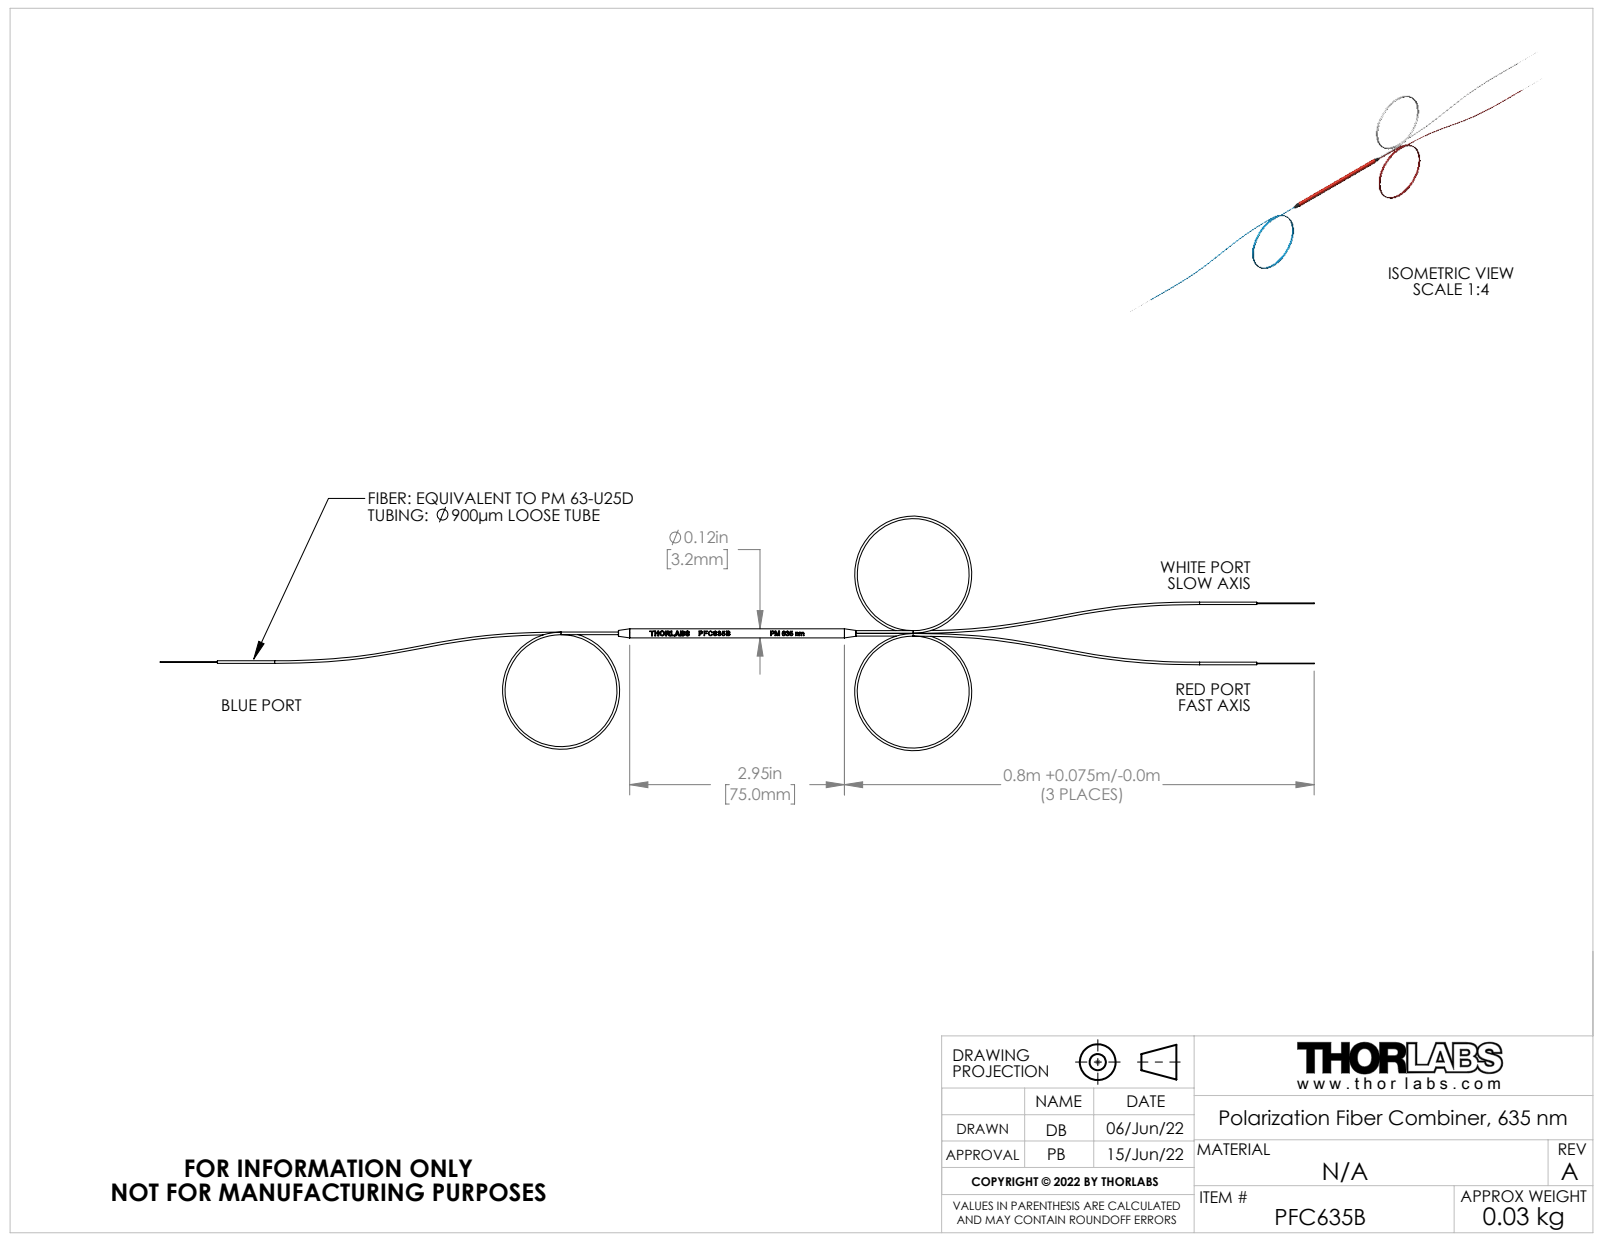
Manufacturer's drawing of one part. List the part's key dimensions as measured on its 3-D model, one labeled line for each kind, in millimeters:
Part name (STEP PRODUCT): T09HBU1_Standard; DWG1631_75mm; PANDA 635_60; T09HNT1_Standard (+8 more)
STEP written by: SolidWorks 2020 (CONFIG_CONTROL_DESIGN)
Units: millimetres
Bodies: 14 solids, 253 faces (41 planar, 150 cylindrical, 62 other)
Overall size (bounding box): 403 × 81.9 × 4.9
Volume: 832 mm³ · Surface area: 7 382 mm²
Round holes (diameter × count): ⌀0.5 ×6, ⌀1 ×2, ⌀0.95 ×1, ⌀2.69 ×1
Round bosses / shafts (diameter × count): ⌀0.9 ×6, ⌀0.25 ×5, ⌀3.15 ×1, ⌀2.5 ×1
Partial cylindrical surfaces — rounded edges, fillets, slot ends (radius × count): R0.45 ×2, R1 ×1
Main face-to-face distances: 3, 69, 6, 72, 66, 75, 63, 58.5, 52.5, 16.5
Hole centre spacings: 10.2, 10.69, 0.5, 11.18, 1, 4.03, 9.71, 20.5
